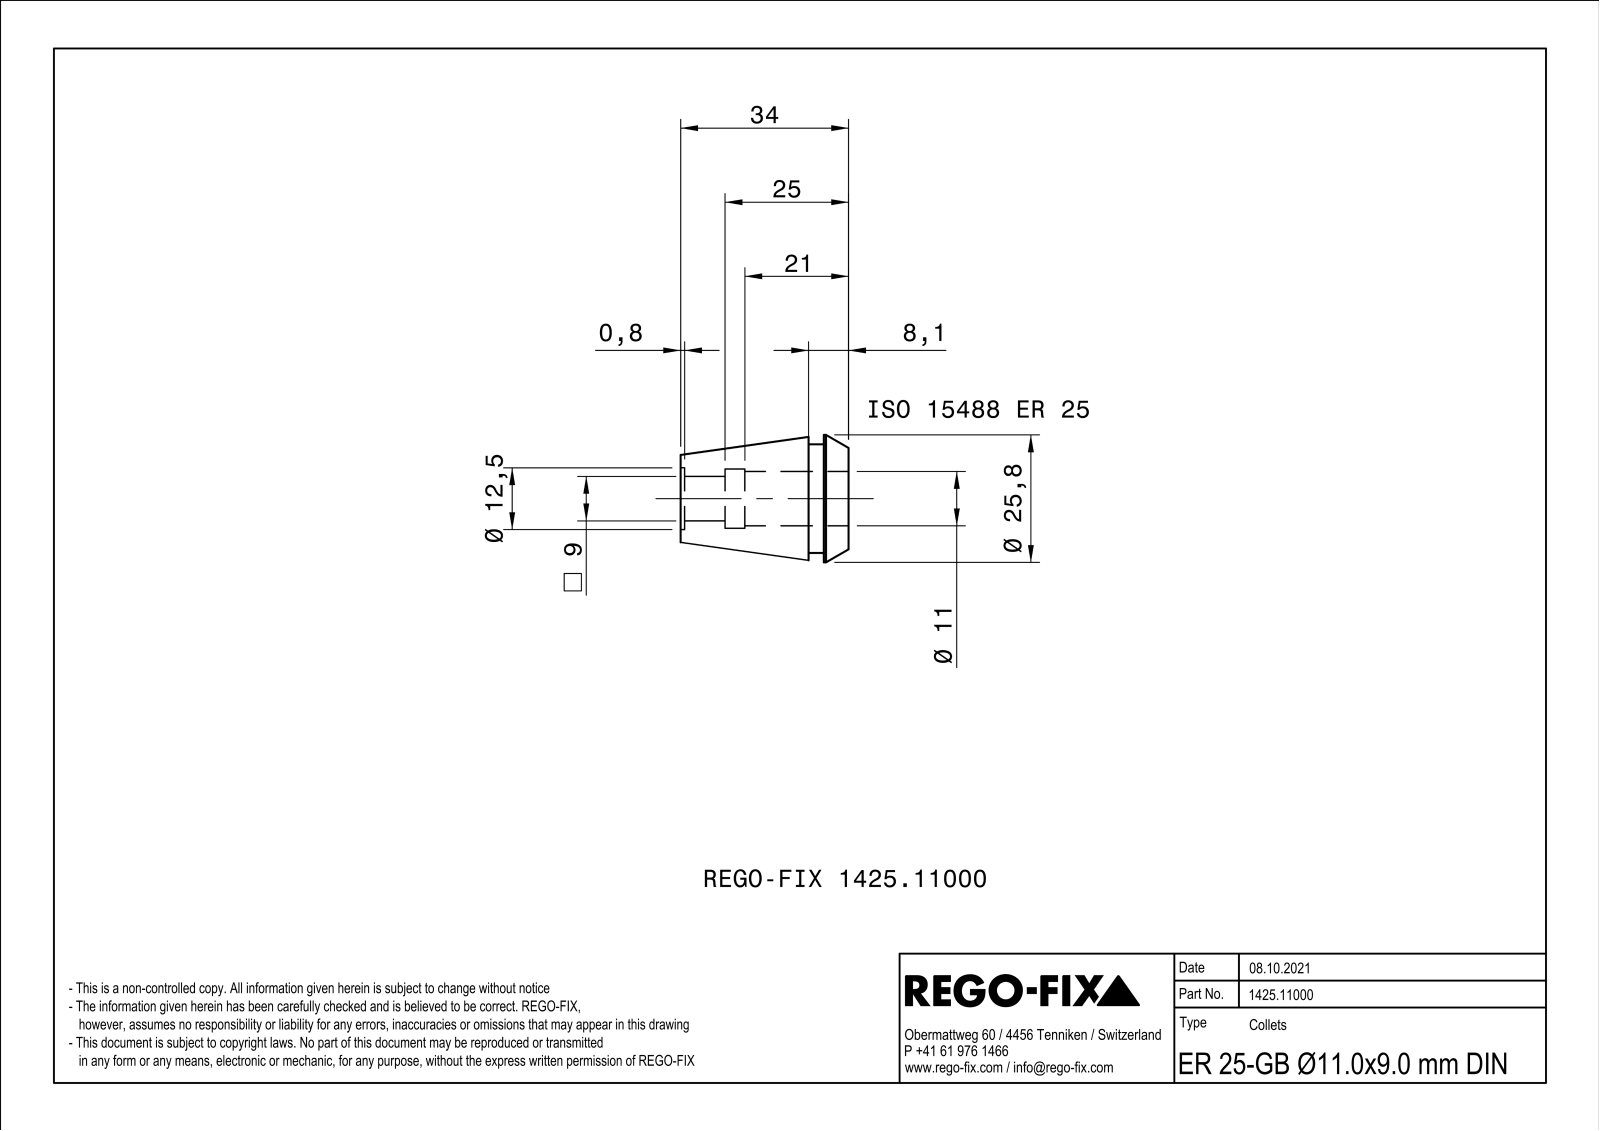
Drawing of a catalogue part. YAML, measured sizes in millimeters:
part_name: "NOCUT"
step_written_by: "SIEMENS PLM Software Solid Edge ST10 (AUTOMOTIVE_DESIGN)"
units: millimeters
bodies: {solids: 1, faces: 140, planar: 60, cylindrical: 36, other: 44}
overall_size: [34, 25.79, 25.79]
volume: 8268
surface_area: 6302
round_holes:
  - {diameter: 11, count: 1}
  - {diameter: 12, count: 1}
round_bosses_or_shafts:
  - {diameter: 25.8, count: 1}
  - {diameter: 22, count: 1}
partial_cylinders:
  - {radius: 5, count: 1}
  - {radius: 5.8, count: 1}
face_to_face_distances: [0.8, 5, 8.1, 3.1, 4.35, 5.15, 9.5, 5.5, 0.5, 2.6]
